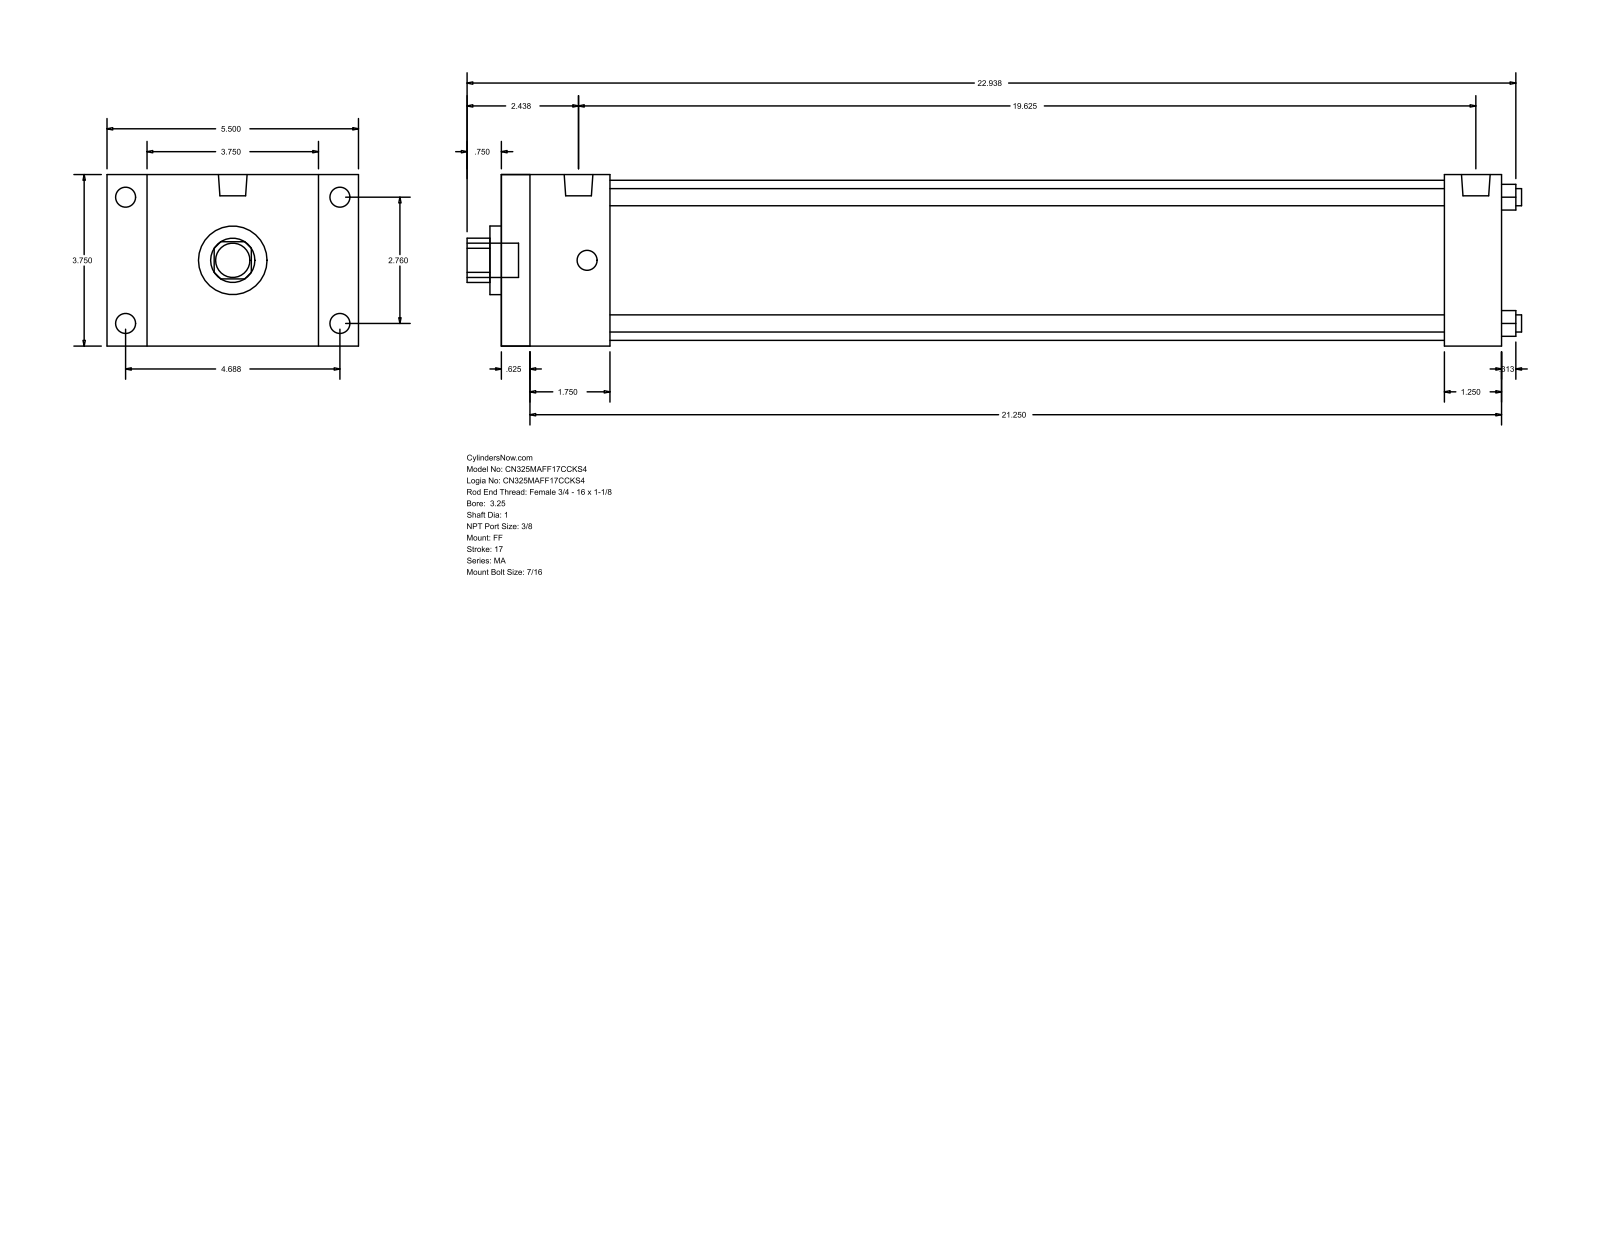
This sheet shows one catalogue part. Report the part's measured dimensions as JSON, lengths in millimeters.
{"part_name": "MA_FF__0325_1", "step_written_by": "GSSL Pune (CONFIG_CONTROL_DESIGN)", "units": "millimeters", "bodies": {"solids": 0, "faces": 92, "planar": 64, "cylindrical": 28, "other": 0}, "overall_size": [585.79, 139.7, 95.25], "round_holes": [[9.53, 4], [25.4, 1], [38.1, 1], [88.9, 1]], "round_bosses_or_shafts": [[11.11, 8], [15.93, 2], [19.05, 1]], "partial_cylinders_radius": [[12.29, 1]], "face_to_face_distances": [95.24, 555.62, 15.87, 539.75, 22.23, 117.47, 60.33, 523.87, 44.46, 508], "hole_center_spacings": [49.57, 70.1, 99.14]}
